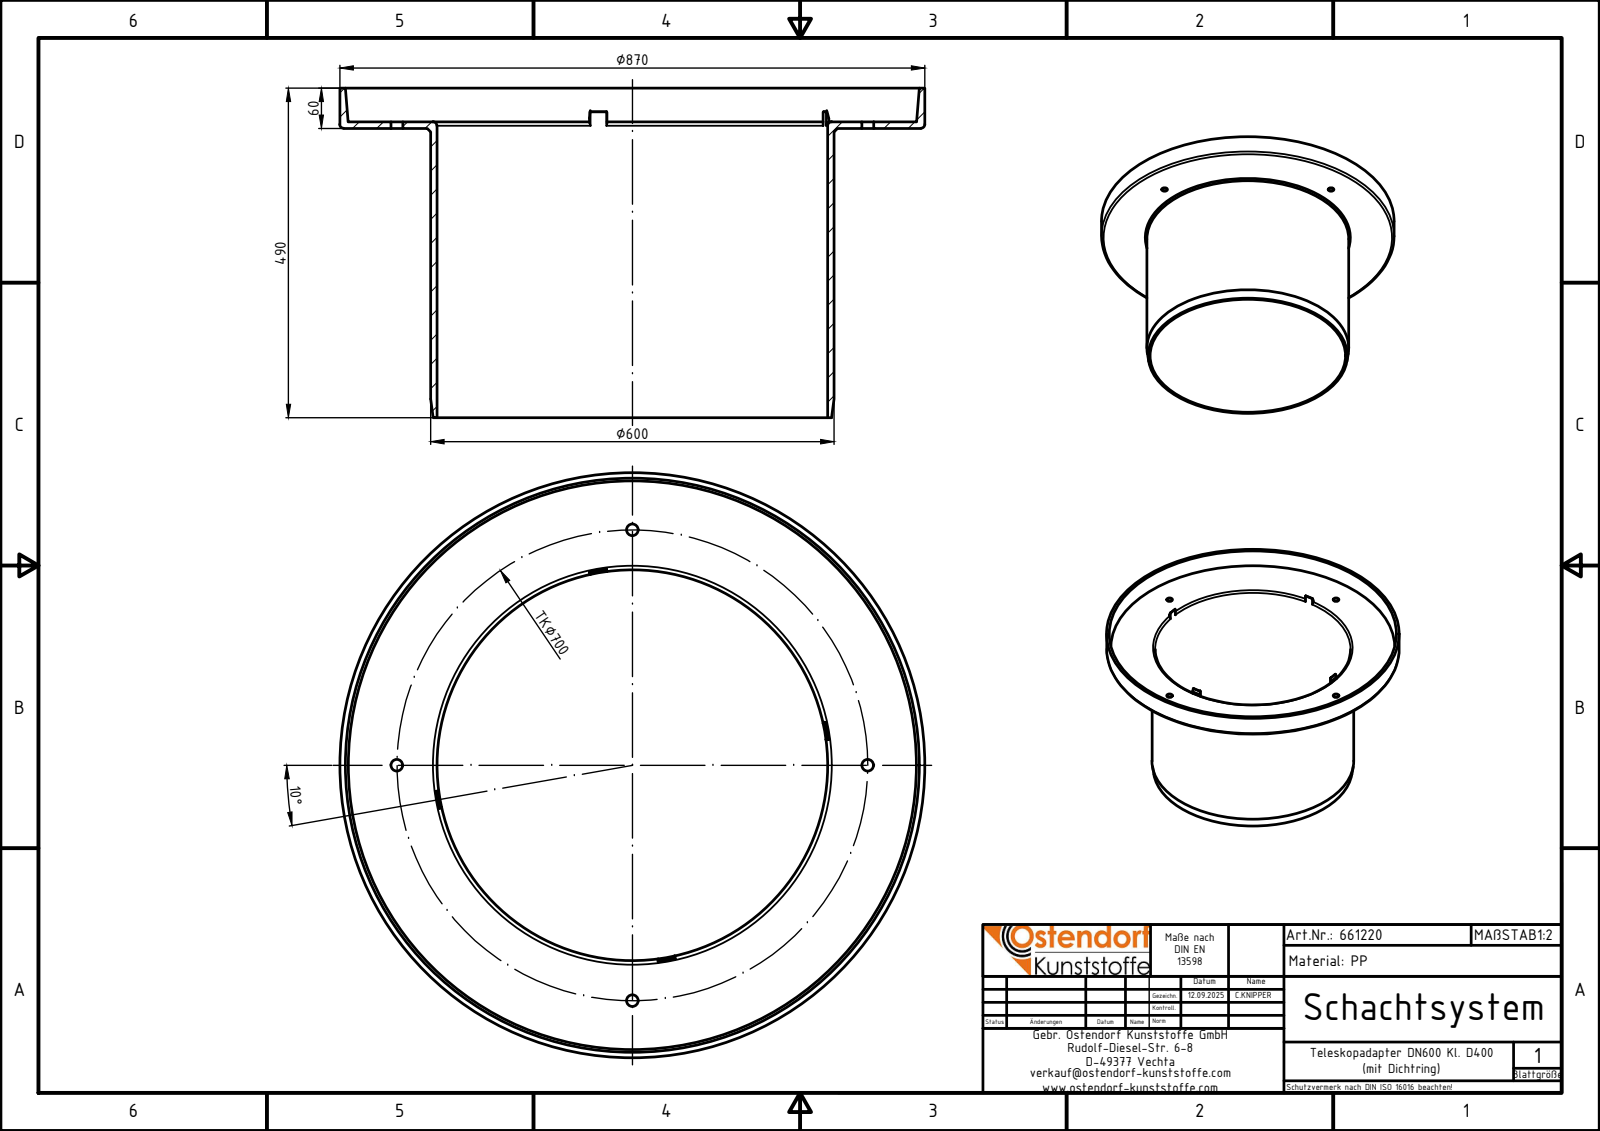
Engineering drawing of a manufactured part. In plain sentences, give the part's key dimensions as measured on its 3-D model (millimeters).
The part is named "661220z". Its 3-D file was written by "Autodesk Inventor 2024 (AUTOMOTIVE_DESIGN)". It is 1 solid with 120 faces: 16 planar, 35 cylindrical and 69 other. Overall it measures 870 by 870 by 490 millimeters. Its volume is 12 150 000 cubic millimeters and its surface area 2 538 000 square millimeters. Round holes: 4 of diameter 17.5, 1 of diameter 581. Round bosses or shafts: 1 of diameter 870, 1 of diameter 600. Partial cylindrical surfaces (rounded edges, fillets, slot ends): 24 of radius 0.5, 1 of radius 294.7. The main face-to-face distances are 10, 60, 50, 430, 440, 490, 455, 25, 15, 35. The hole center spacings are 350, 494.97, 700.
